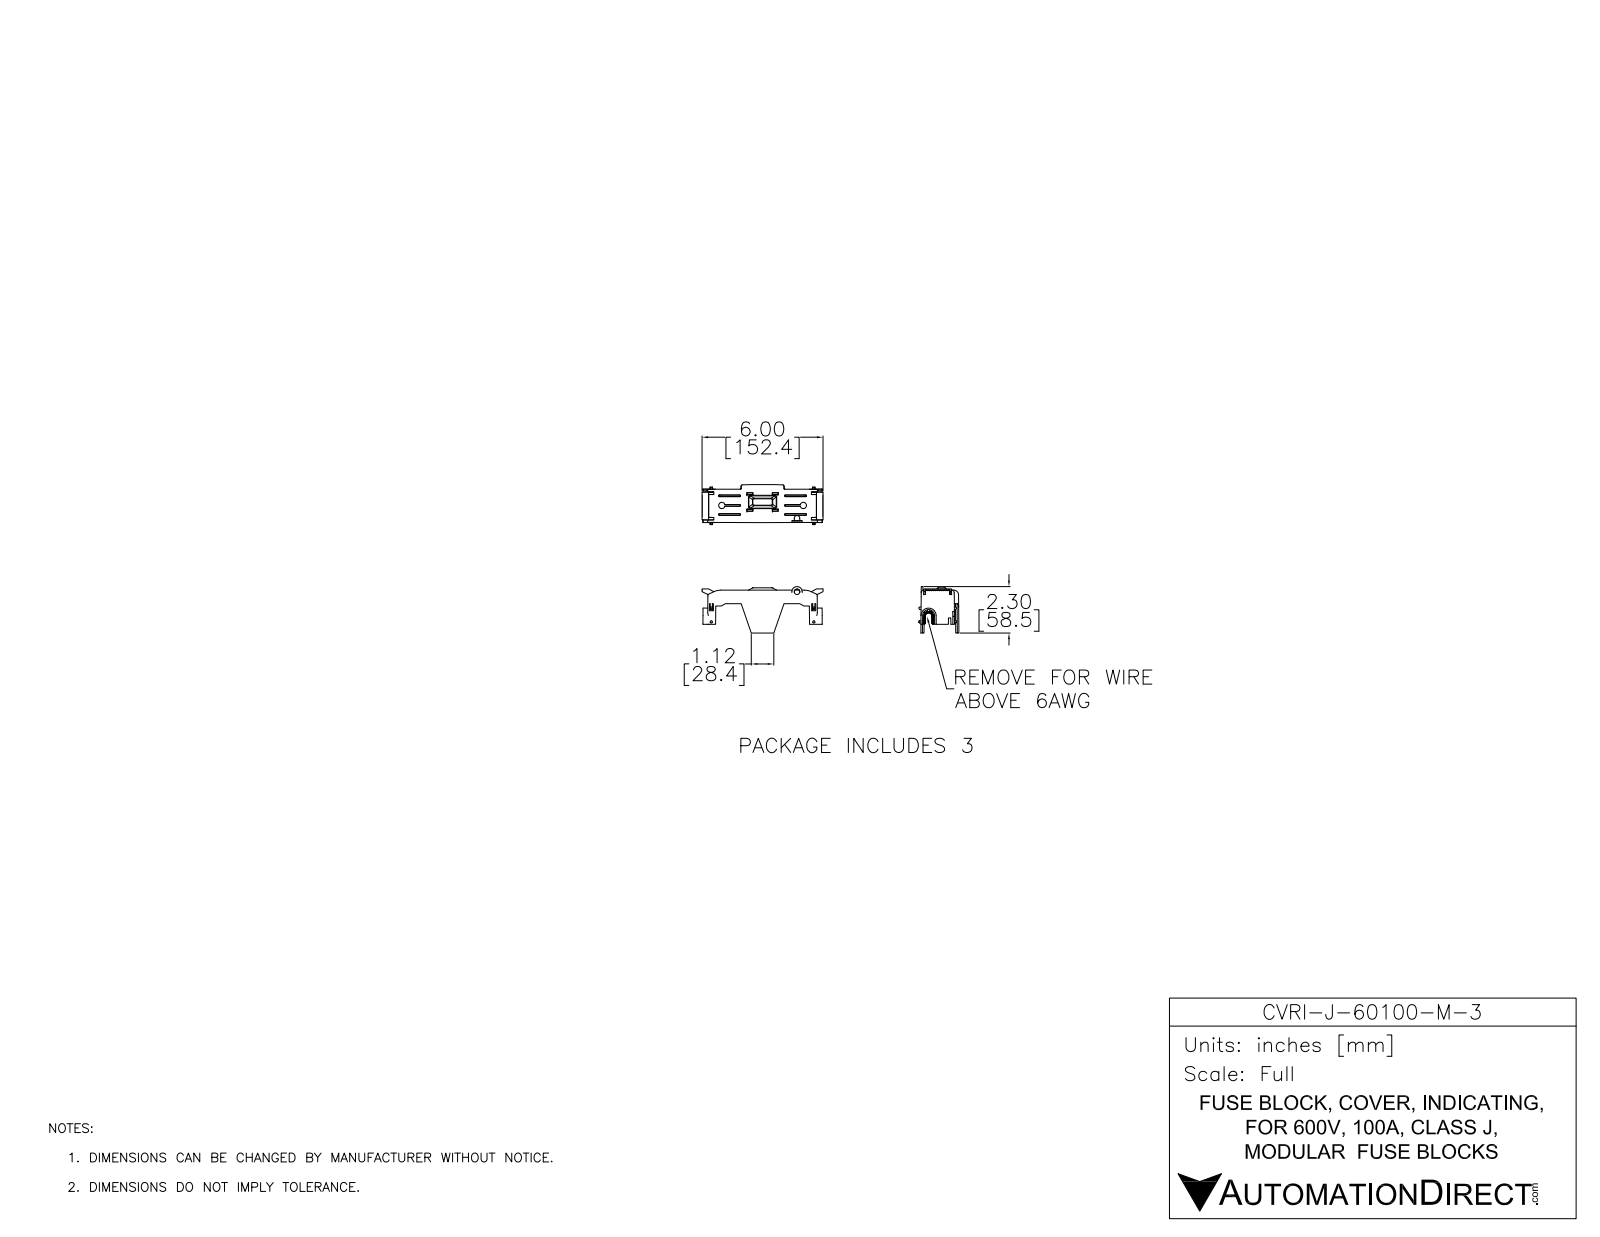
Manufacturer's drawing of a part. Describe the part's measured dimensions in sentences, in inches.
The part is named "CVRI-J-60100-M-3". Its 3-D file was written by "SolidWorks 2017 (AUTOMOTIVE_DESIGN)". It is 1 solid with 1410 faces: 917 planar, 102 cylindrical and 391 other. Overall it measures 5.979 by 2.304 by 1.984 inches. Its volume is 2.55 cubic inches and its surface area 70.01 square inches. Partial cylindrical surfaces (rounded edges, fillets, slot ends): 19 of radius 0.039, 14 of radius 0.118, 6 of radius 0.031, 4 of radius 0.059, 2 of radius 0.01, 2 of radius 0.02, 2 of radius 0.138, 2 of radius 0.169. The main face-to-face distances are 0.079, 0.217, 0.138, 0.295, 0.118, 0.347, 0.197, 0.236, 0.14, 0.061.
